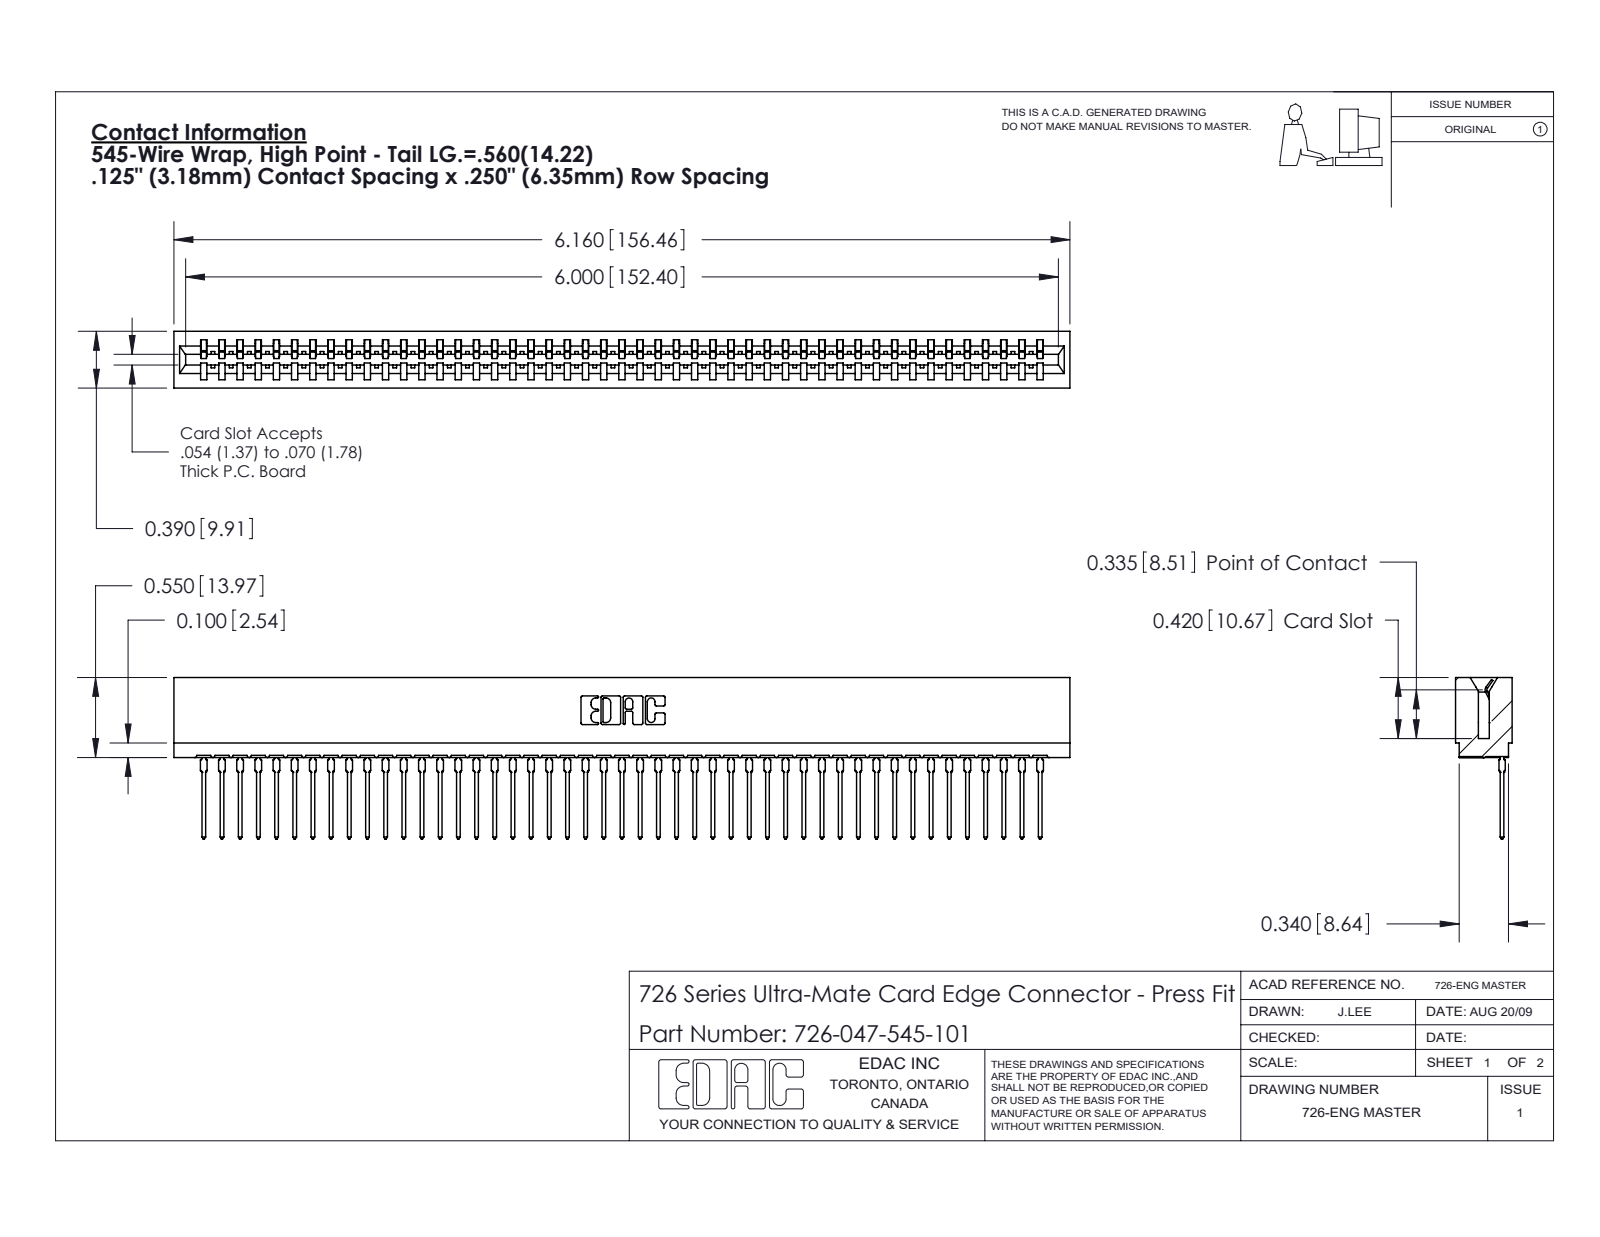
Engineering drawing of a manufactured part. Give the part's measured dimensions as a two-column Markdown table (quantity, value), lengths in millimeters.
| quantity | value |
| --- | --- |
| part name | 726 Part_.515 Slot Depth - 01; 746-292-001_545; 726-047-545-101 |
| STEP written by | SolidWorks 2020 (CONFIG_CONTROL_DESIGN) |
| units | millimeters |
| bodies | 48 solids, 5173 faces (3016 planar, 935 cylindrical, 1222 other) |
| overall size | 156.5 × 28.2 × 9.9 |
| volume | 14 100 mm³ |
| surface area | 22 210 mm² |
| partial cylindrical surfaces (radius × count) | 0.5 × 94, 0.4 × 48, 0.3 × 22, 0.2 × 6, 0.8 × 6, 0.1 × 4, 0.3 × 4, 0.7 × 3 |
| main face-to-face distances | 1.4, 8.5, 9.9, 0.6, 7.8, 6.4, 2.1, 7, 9.3, 0.8 |
